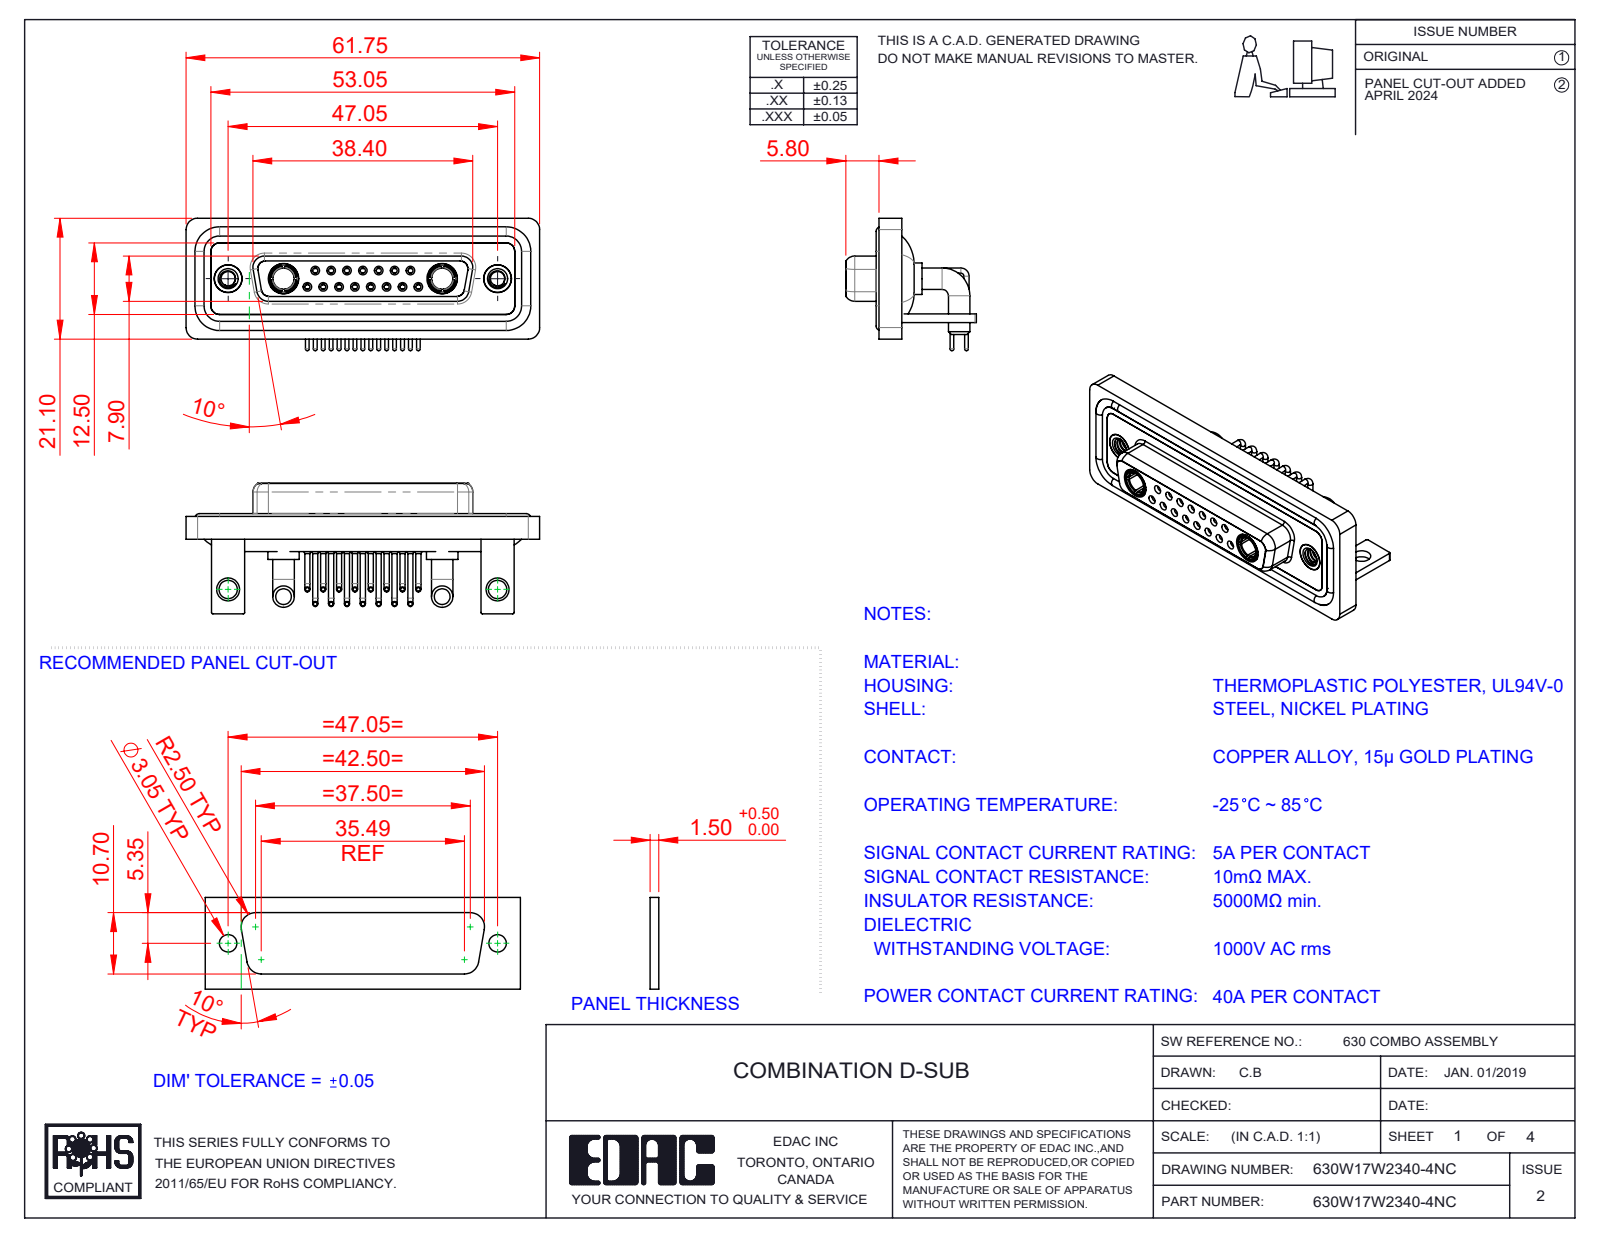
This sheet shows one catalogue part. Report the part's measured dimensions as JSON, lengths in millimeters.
{"part_name": "Power Socket_40A RA; 630Combo Shell Rear_25 Contacts; 630Combo Contact Row 2_50 Contacts; 630Combo Threaded Rivet_A (+6 more)", "step_written_by": "SolidWorks 2023 (CONFIG_CONTROL_DESIGN)", "units": "millimeters", "bodies": {"solids": 28, "faces": 1379, "planar": 408, "cylindrical": 605, "other": 366}, "overall_size": [61.75, 23.12, 22.8], "volume_mm3": 8991, "surface_area_mm2": 15356, "round_holes": [[0.9, 15], [1.1, 15], [1.5, 15], [2, 15], [1.6, 8], [1.7, 7], [4.85, 4], [2.5, 2], [3.2, 2], [3.7, 2], [4, 2], [4.05, 2]], "round_bosses_or_shafts": [[0.9, 15], [0.65, 15], [1.6, 11], [3.75, 4], [5.5, 2], [5.2, 2], [4.96, 2], [4.95, 2]], "partial_cylinders_radius": [[2, 19], [1.5, 18], [0.25, 16], [1.35, 8], [1.6, 8], [0.5, 5], [0.6, 4], [0.65, 4]], "face_to_face_distances": [0.4, 1.8, 2.9, 3.7, 1.5, 4.1, 1.1, 1.4, 1.6, 3.1], "hole_center_spacings": [3.16, 2.77, 5.54, 8.31, 5.04, 7.49, 11.08, 5.03]}
